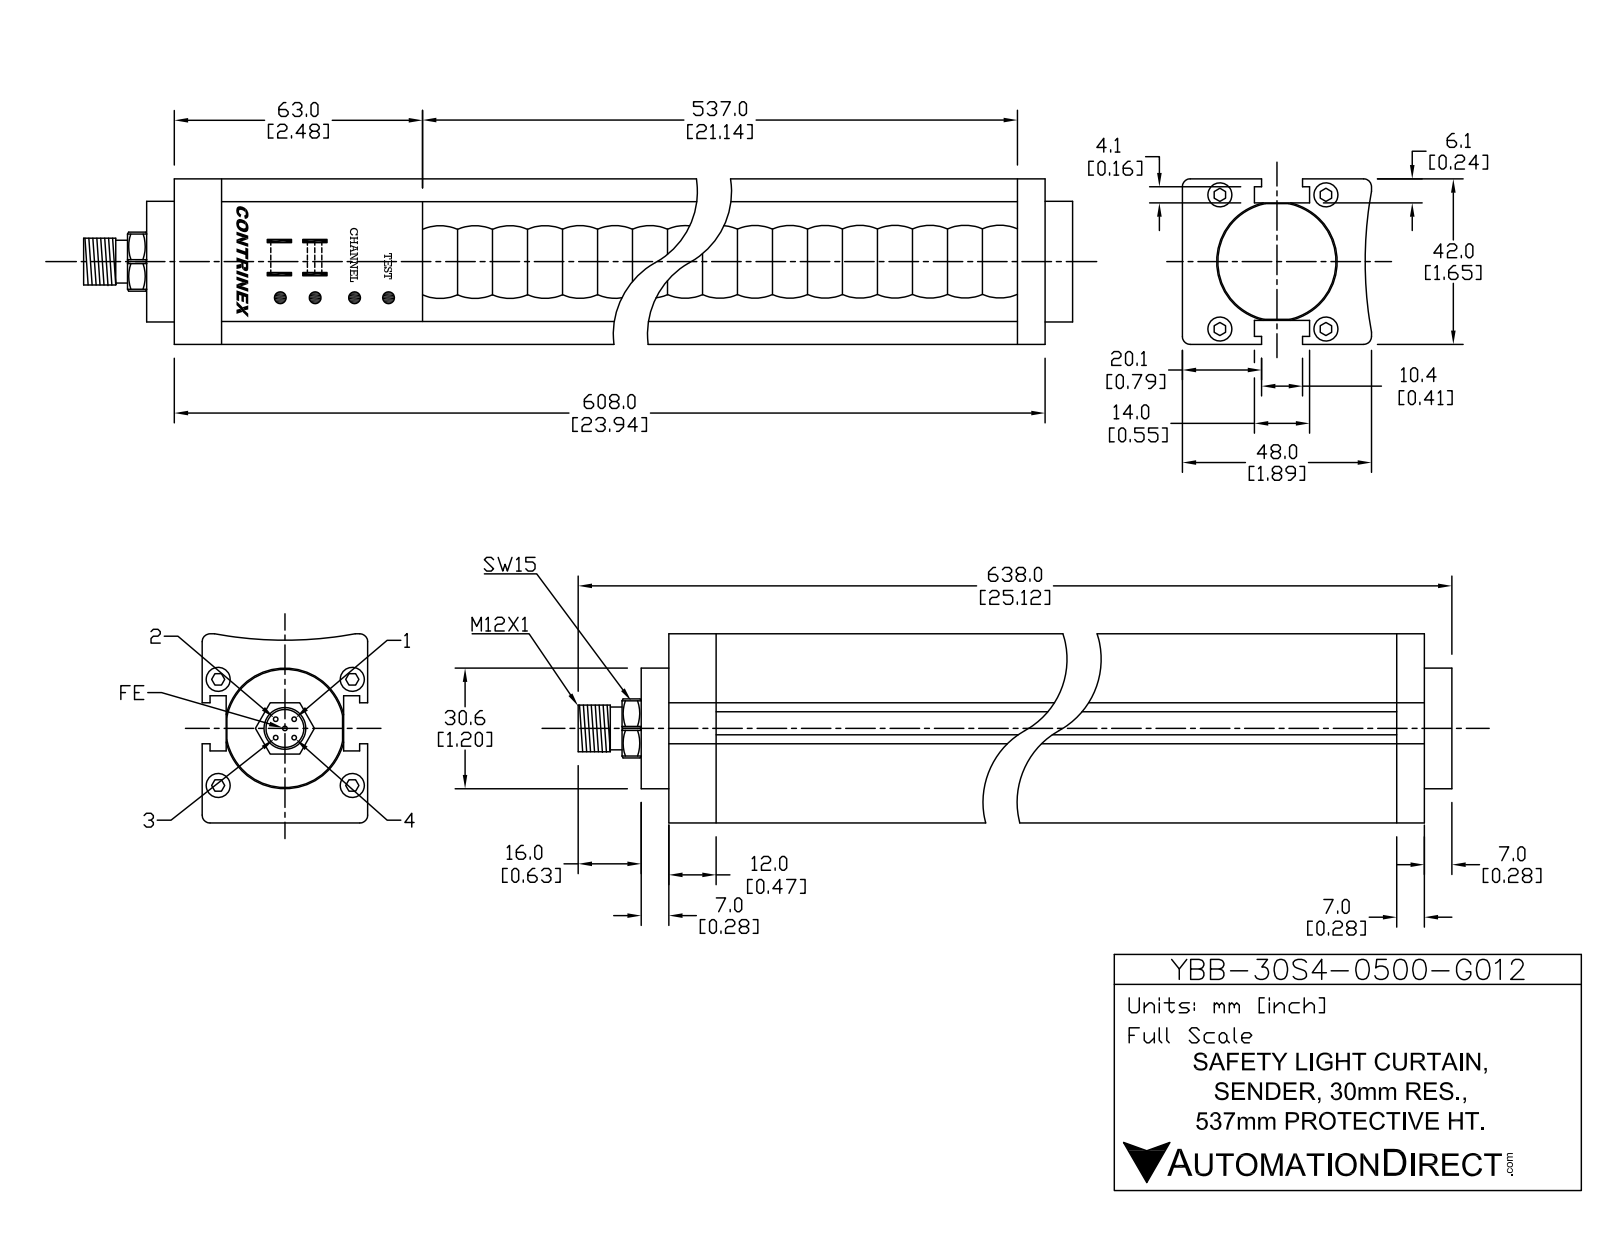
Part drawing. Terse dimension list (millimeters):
name: YBB-30S4-0500-G012
written by: SolidWorks 2016 (AUTOMOTIVE_DESIGN)
unit: mm
bodies: 19 solids, 440 faces (208 planar, 168 cylindrical, 64 other)
size: 638 × 48 × 42
volume: 1 099 000 mm³; area: 147 436 mm²
holes: 4× ⌀6, 1× ⌀8.5, 1× ⌀32
bosses: 5× ⌀1, 4× ⌀5.5, 1× ⌀30.6, 1× ⌀12, 1× ⌀10.5
rounds: 48× R1, 4× R0.5, 2× R0.55, 1× R8.2, 1× R100
face distances: 6.3, 35.7, 42, 29.4, 14, 17.2, 31.2, 588, 15.7, 29.7
hole spacings: 21.04, 22.34, 26.9, 34, 43.35
